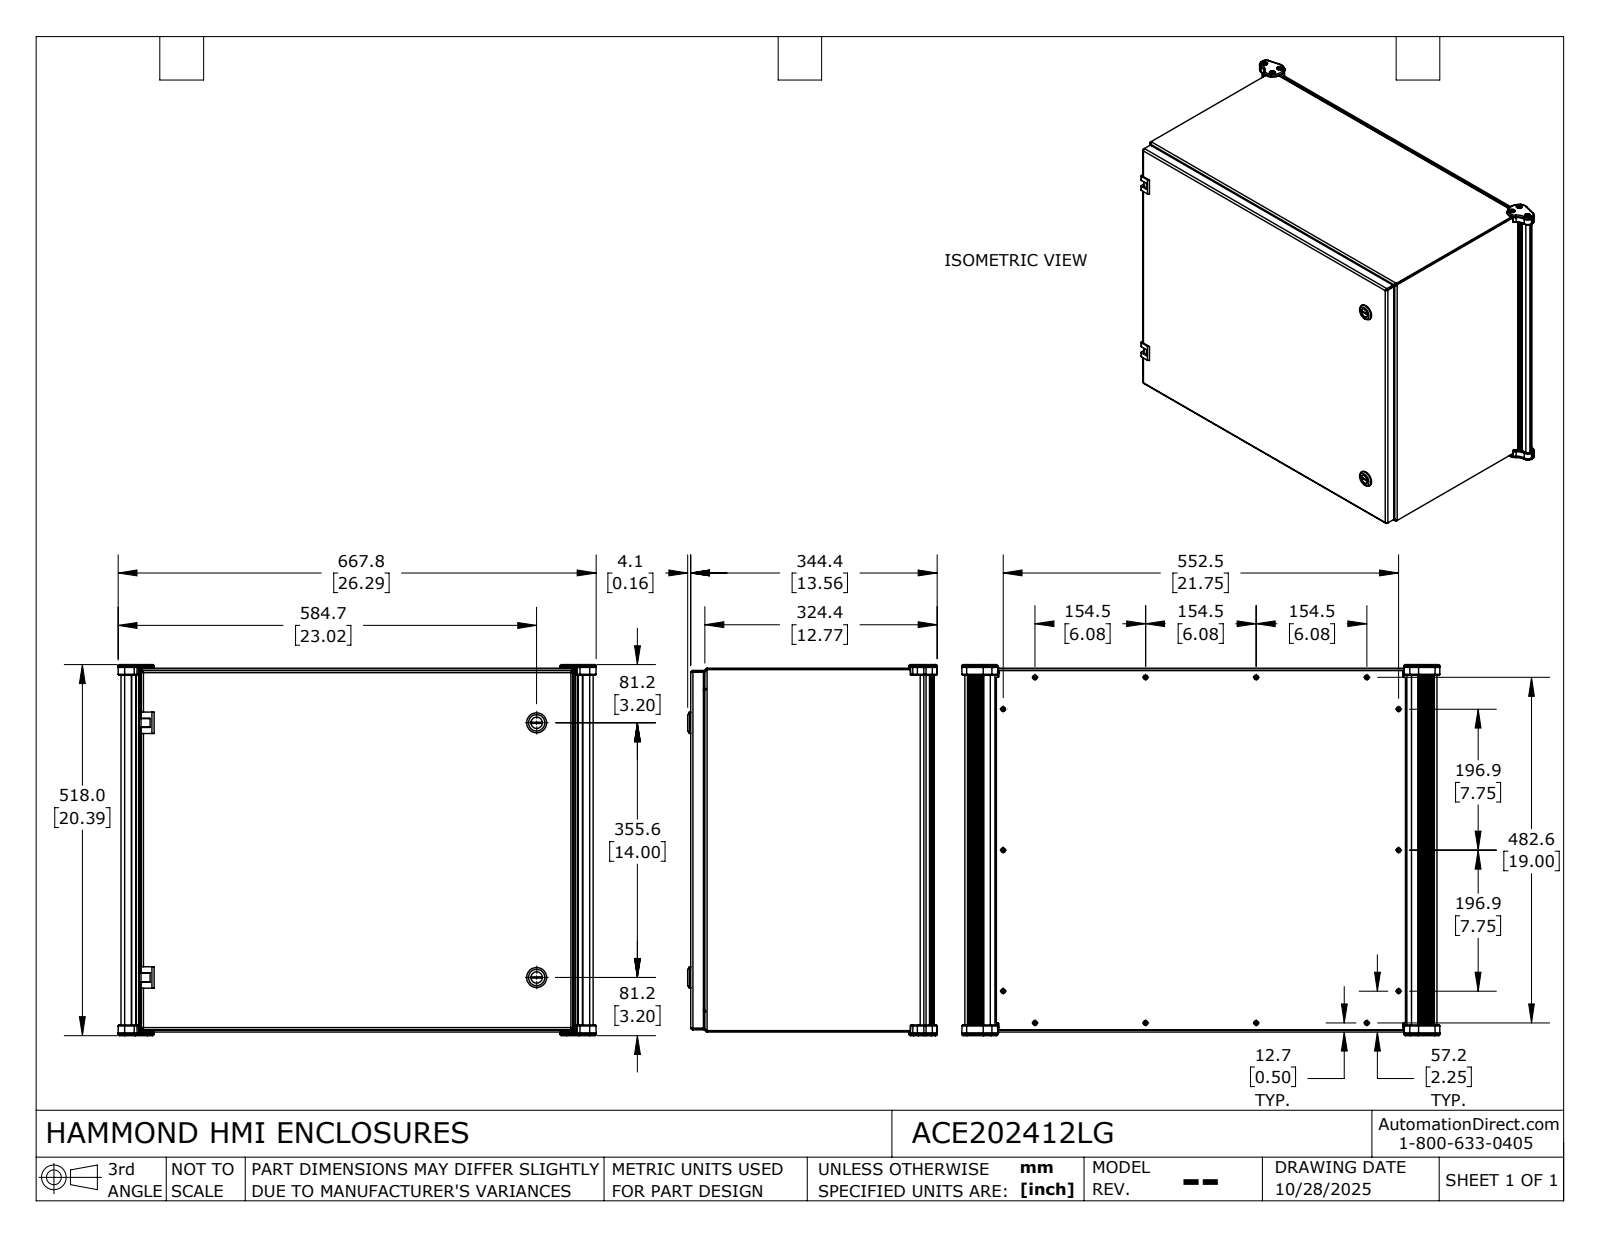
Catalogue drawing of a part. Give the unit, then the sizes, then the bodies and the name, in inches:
Units: inches
Overall size (bounding box): 26.292 × 20.395 × 13.719
Round holes (diameter × count): ⌀0.156 ×16, ⌀0.234 ×16, ⌀0.19 ×14, ⌀0.205 ×6, ⌀0.413 ×6, ⌀0.196 ×5, ⌀0.159 ×4, ⌀0.406 ×4, ⌀0.16 ×2, ⌀0.197 ×2, ⌀0.232 ×2, ⌀0.25 ×2
Round bosses / shafts (diameter × count): ⌀0.256 ×14, ⌀0.25 ×6, ⌀0.19 ×6, ⌀0.149 ×6, ⌀0.236 ×5, ⌀0.375 ×4, ⌀0.33 ×4, ⌀1.1 ×2
Partial cylindrical surfaces — rounded edges, fillets, slot ends (radius × count): R0.01 ×38, R0.059 ×30, R0.041 ×18, R0.121 ×18, R0.016 ×16, R0.03 ×16, R0.05 ×16, R0.039 ×14
Main face-to-face distances: 0.081, 19.919, 12.831, 0.125, 23.919, 0.125, 12.912, 12.956, 13.037, 0.206
Hole centre spacings: 19.95, 2.475, 6.083, 7.75, 8.026, 9.66, 11.8, 12.167
Volume: 263.3 in³ · Surface area: 5 799 in²
Bodies: 105 solids, 2608 faces (1232 planar, 871 cylindrical, 505 other)
Part name (STEP PRODUCT): ACE202412LG
STEP written by: SolidWorks 2024 (AUTOMOTIVE_DESIGN)
